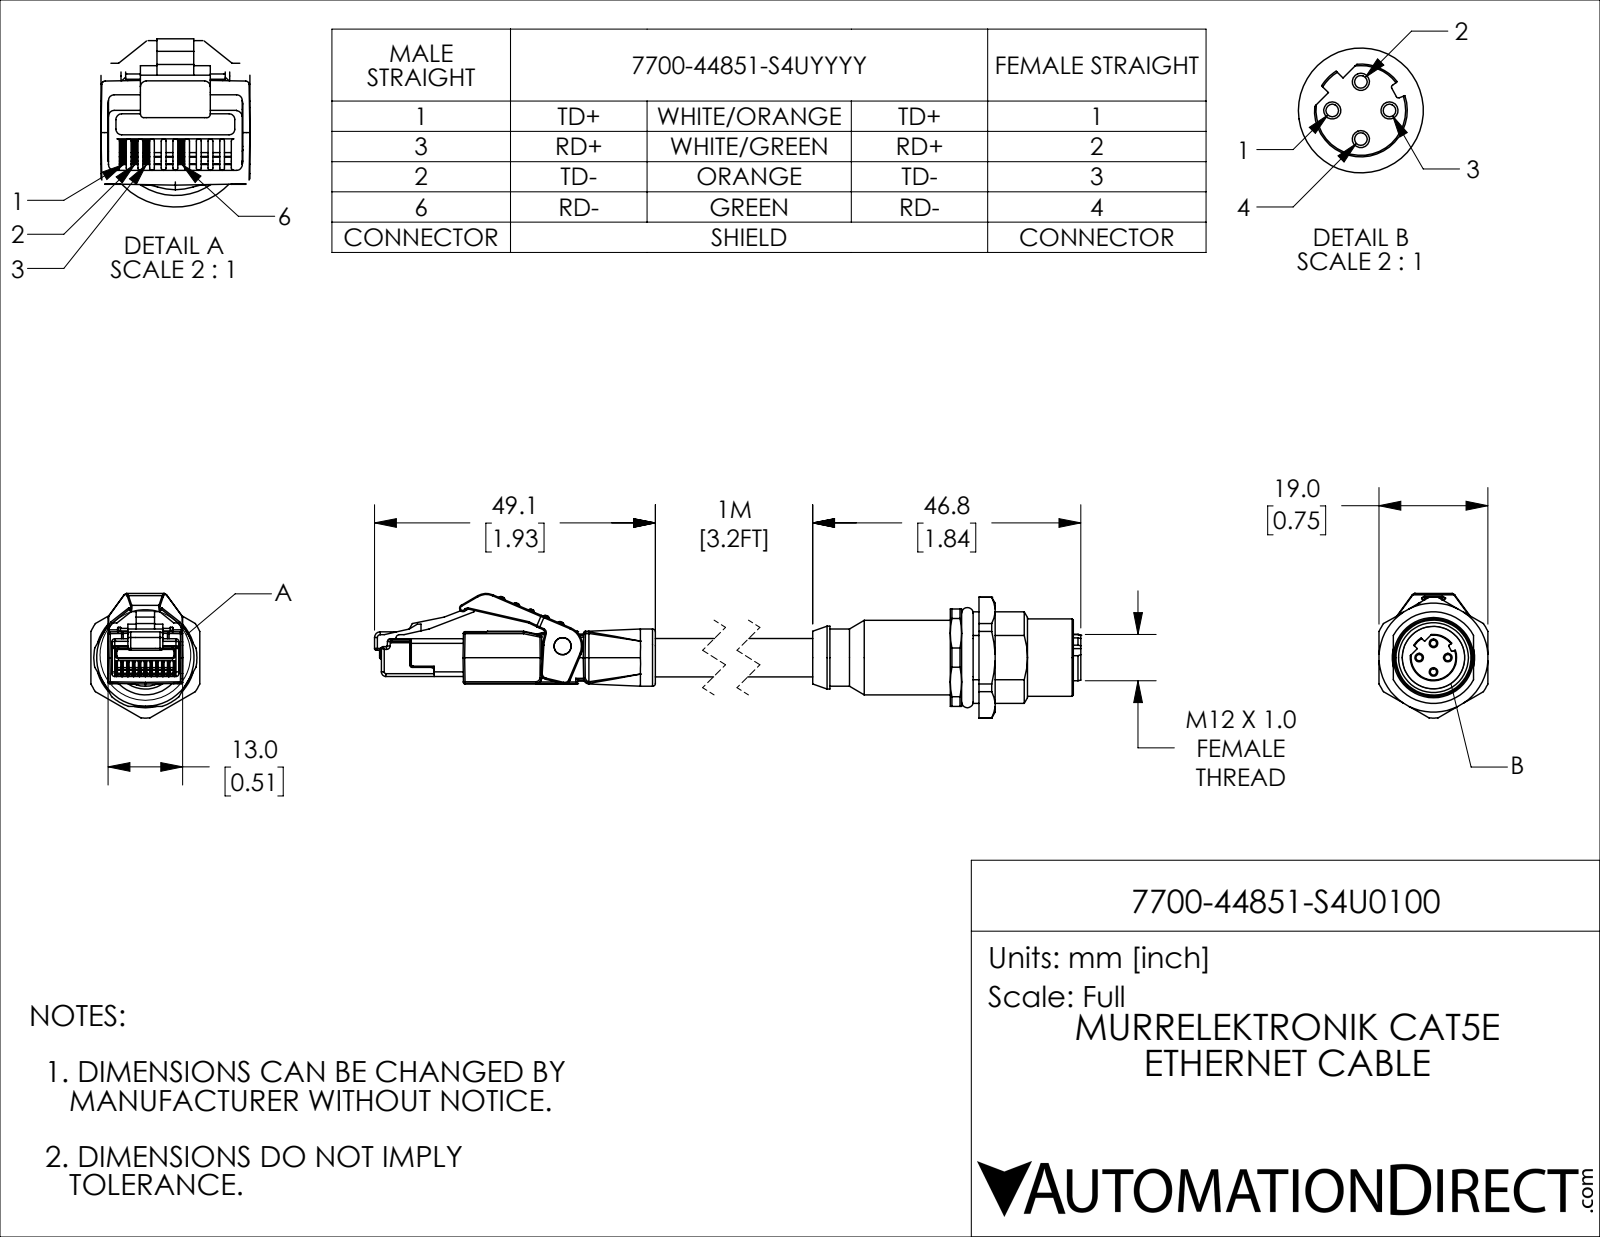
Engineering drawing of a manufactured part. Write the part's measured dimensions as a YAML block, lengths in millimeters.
part_name: "7700-44851-S4U0100; 7700-44851-S4U0100_NUT; 7700-44851-S4U0100_1; 7700-44851-S4U0100_2"
step_written_by: "SolidWorks 2021 (CONFIG_CONTROL_DESIGN)"
units: millimeters
bodies: {solids: 3, faces: 838, planar: 325, cylindrical: 331, other: 182}
overall_size: [134.9, 21.7, 19]
volume: 13000
surface_area: 7471
round_holes:
  - {diameter: 1.1, count: 4}
  - {diameter: 3, count: 1}
  - {diameter: 10.9, count: 1}
  - {diameter: 12.2, count: 1}
  - {diameter: 14.4, count: 1}
round_bosses_or_shafts:
  - {diameter: 13.5, count: 1}
  - {diameter: 13, count: 1}
  - {diameter: 11, count: 1}
  - {diameter: 10, count: 1}
  - {diameter: 6.7, count: 1}
  - {diameter: 3, count: 1}
partial_cylinders:
  - {radius: 0.2, count: 83}
  - {radius: 0.3, count: 64}
  - {radius: 0.5, count: 24}
  - {radius: 0.1, count: 20}
  - {radius: 0.8, count: 5}
  - {radius: 1, count: 5}
  - {radius: 2, count: 2}
  - {radius: 5, count: 2}
face_to_face_distances: [13, 9.2, 0.5, 13.5, 2.8, 5, 7.8, 1.1, 12.9, 0.6]
hole_center_spacings: [2.5, 3.5, 5]
